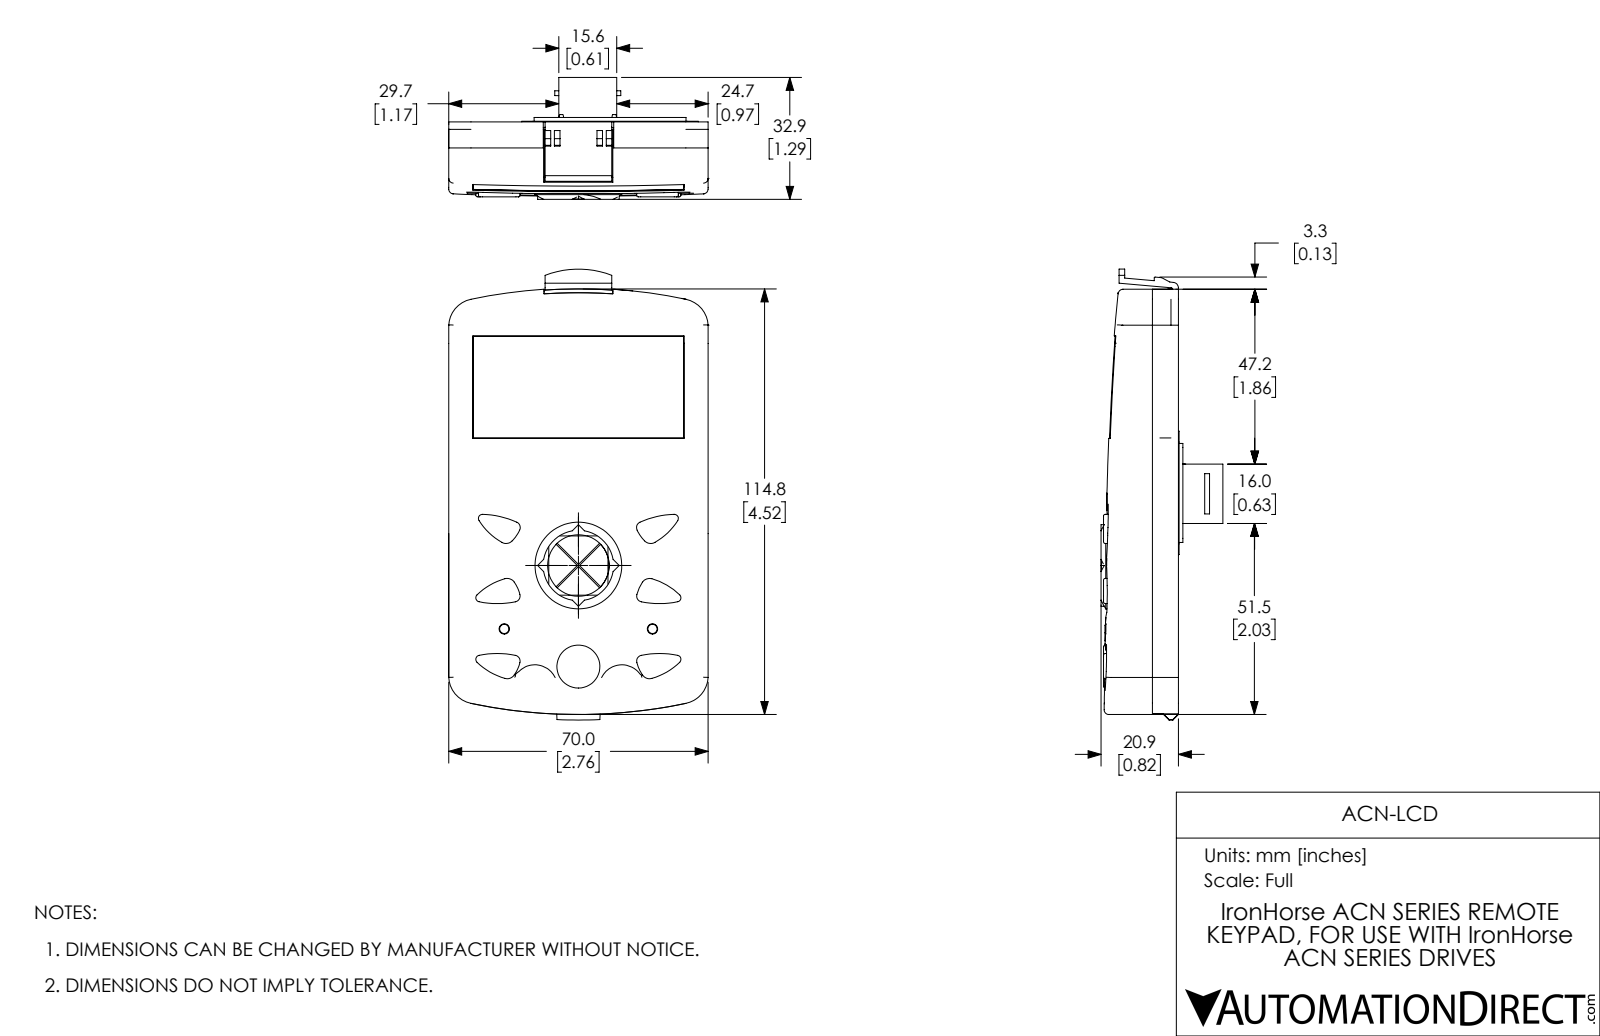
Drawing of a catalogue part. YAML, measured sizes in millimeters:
part_name: "ACN-LCD - Coord"
step_written_by: "SolidWorks 2017 (AUTOMOTIVE_DESIGN)"
units: millimeters
bodies: {solids: 21, faces: 1184, planar: 527, cylindrical: 320, other: 337}
overall_size: [121.6, 70, 32.9]
volume: 143200
surface_area: 69610
round_holes:
  - {diameter: 1.3, count: 6}
  - {diameter: 4.3, count: 3}
  - {diameter: 1, count: 2}
  - {diameter: 2.8, count: 2}
  - {diameter: 3, count: 2}
  - {diameter: 3.5, count: 2}
  - {diameter: 5.5, count: 2}
  - {diameter: 11.1, count: 1}
  - {diameter: 16.6, count: 1}
  - {diameter: 23.1, count: 1}
round_bosses_or_shafts:
  - {diameter: 5, count: 11}
  - {diameter: 3.8, count: 4}
  - {diameter: 5.3, count: 3}
  - {diameter: 4, count: 3}
  - {diameter: 2.5, count: 3}
  - {diameter: 6, count: 2}
  - {diameter: 5.5, count: 2}
  - {diameter: 4.5, count: 2}
partial_cylinders:
  - {radius: 1, count: 12}
  - {radius: 1.1, count: 12}
  - {radius: 0.5, count: 9}
  - {radius: 7.6, count: 8}
  - {radius: 0.8, count: 6}
  - {radius: 1.3, count: 6}
  - {radius: 1.6, count: 6}
  - {radius: 2.1, count: 6}
face_to_face_distances: [1.5, 1.4, 1, 1.6, 6.8, 6.6, 0.6, 5.2, 5.1, 8.2]
hole_center_spacings: [35.4, 45.9, 18.1, 20, 20, 21.6, 22.4, 26.3]
